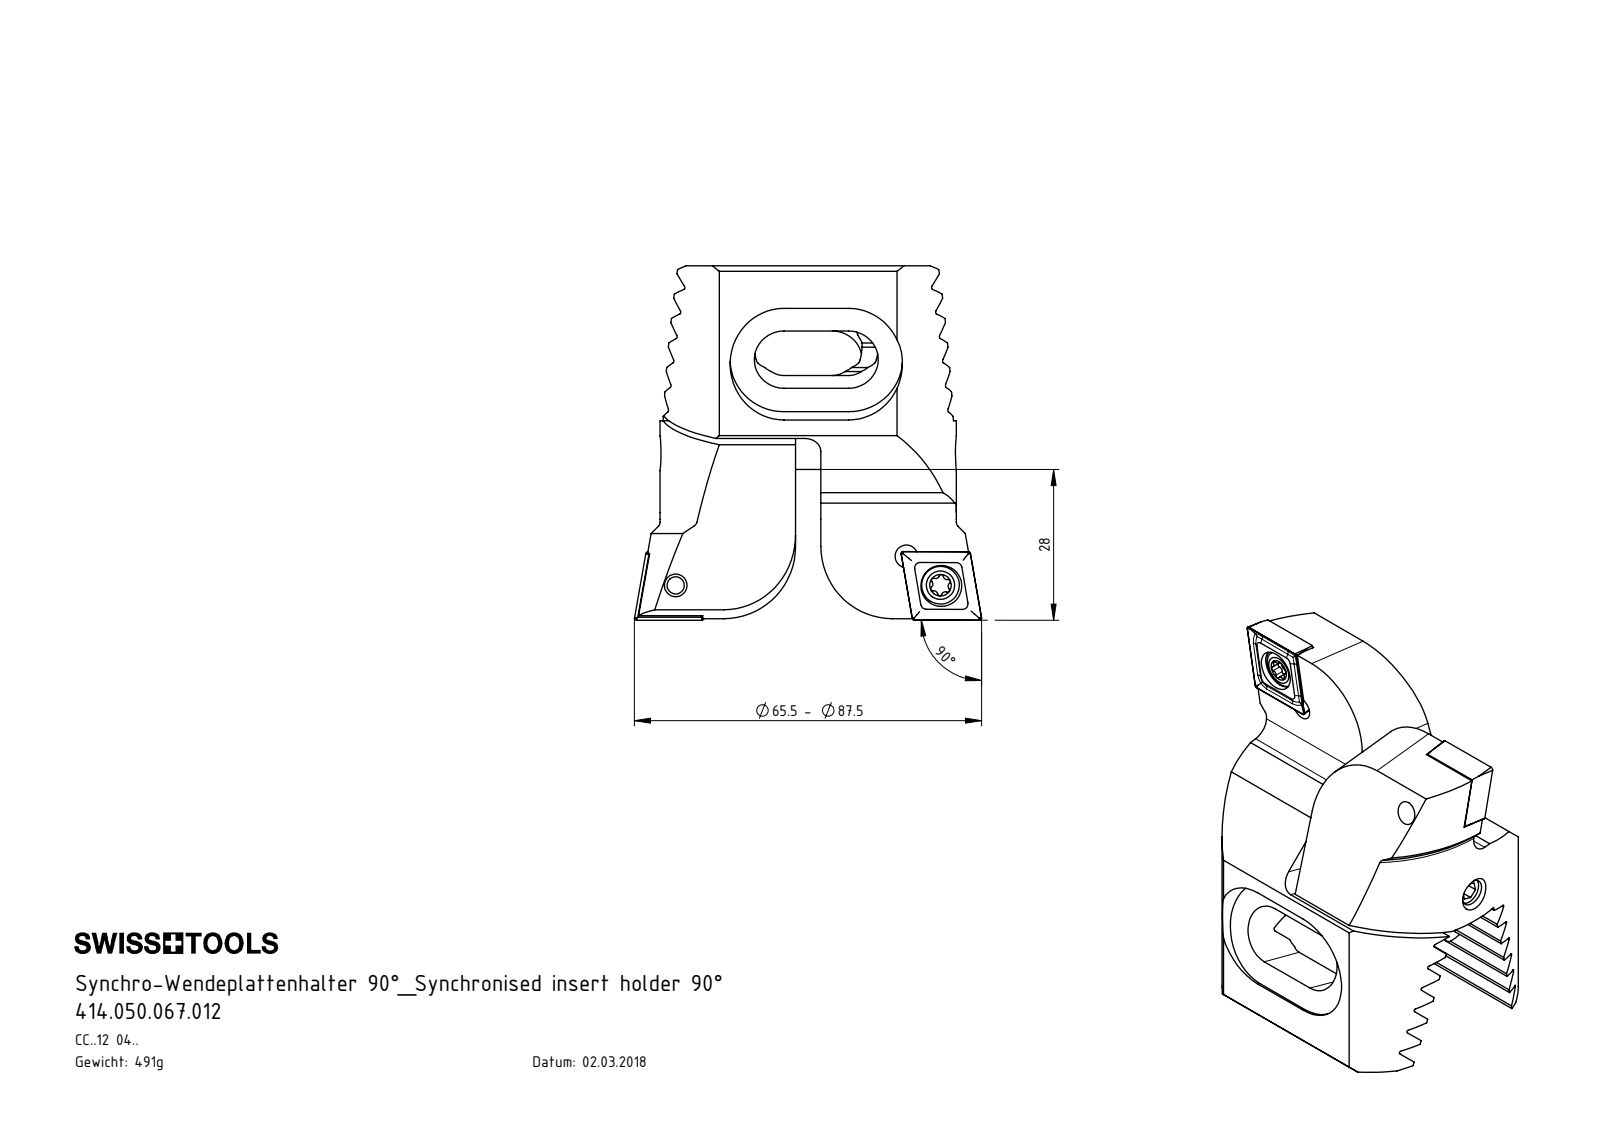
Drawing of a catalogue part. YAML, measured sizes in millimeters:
part_name: "414.050.067.012; WCC-ER2.001.010_A; ISO 4026 - M4 x 5; CCMT120404 (+4 more)"
step_written_by: "SolidWorks 2017 (CONFIG_CONTROL_DESIGN)"
units: millimeters
bodies: {solids: 11, faces: 484, planar: 187, cylindrical: 155, other: 142}
overall_size: [65.75, 64.42, 44]
volume: 62568
surface_area: 24121
round_holes:
  - {diameter: 4.2, count: 4}
  - {diameter: 1, count: 3}
  - {diameter: 3.3, count: 3}
  - {diameter: 5.5, count: 2}
  - {diameter: 7.6, count: 2}
  - {diameter: 5, count: 1}
round_bosses_or_shafts:
  - {diameter: 4, count: 3}
  - {diameter: 7, count: 2}
  - {diameter: 5, count: 2}
  - {diameter: 17, count: 1}
  - {diameter: 6, count: 1}
  - {diameter: 3.8, count: 1}
partial_cylinders:
  - {radius: 0.34, count: 12}
  - {radius: 0.39, count: 12}
  - {radius: 0.69, count: 12}
  - {radius: 1, count: 8}
  - {radius: 3, count: 4}
  - {radius: 5.5, count: 4}
  - {radius: 10, count: 4}
  - {radius: 13.3, count: 2}
face_to_face_distances: [4.07, 8.14, 12.21, 16.28, 20.35, 4.85, 17.24, 1, 7.12, 21.7]
hole_center_spacings: [8.29, 3, 8.49, 8.5, 14.99, 15, 15.3, 28.36]
